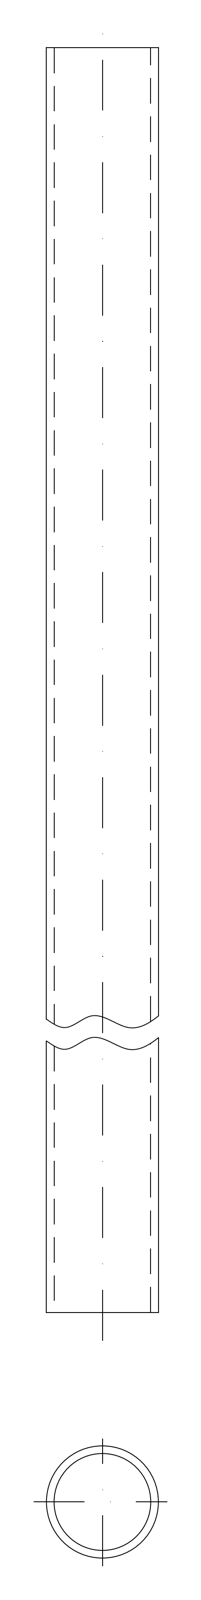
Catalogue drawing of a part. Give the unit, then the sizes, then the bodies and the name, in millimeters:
Units: millimetres
Overall size (bounding box): 248 × 22 × 22
Round holes (diameter × count): ⌀19 ×1
Round bosses / shafts (diameter × count): ⌀22 ×1
Main face-to-face distances: 248
Volume: 23 958 mm³ · Surface area: 32 137 mm²
Bodies: 1 solid, 4 faces (2 planar, 2 cylindrical, 0 other)
STEP written by: THINKDESIGN (CONFIG_CONTROL_DESIGN)
